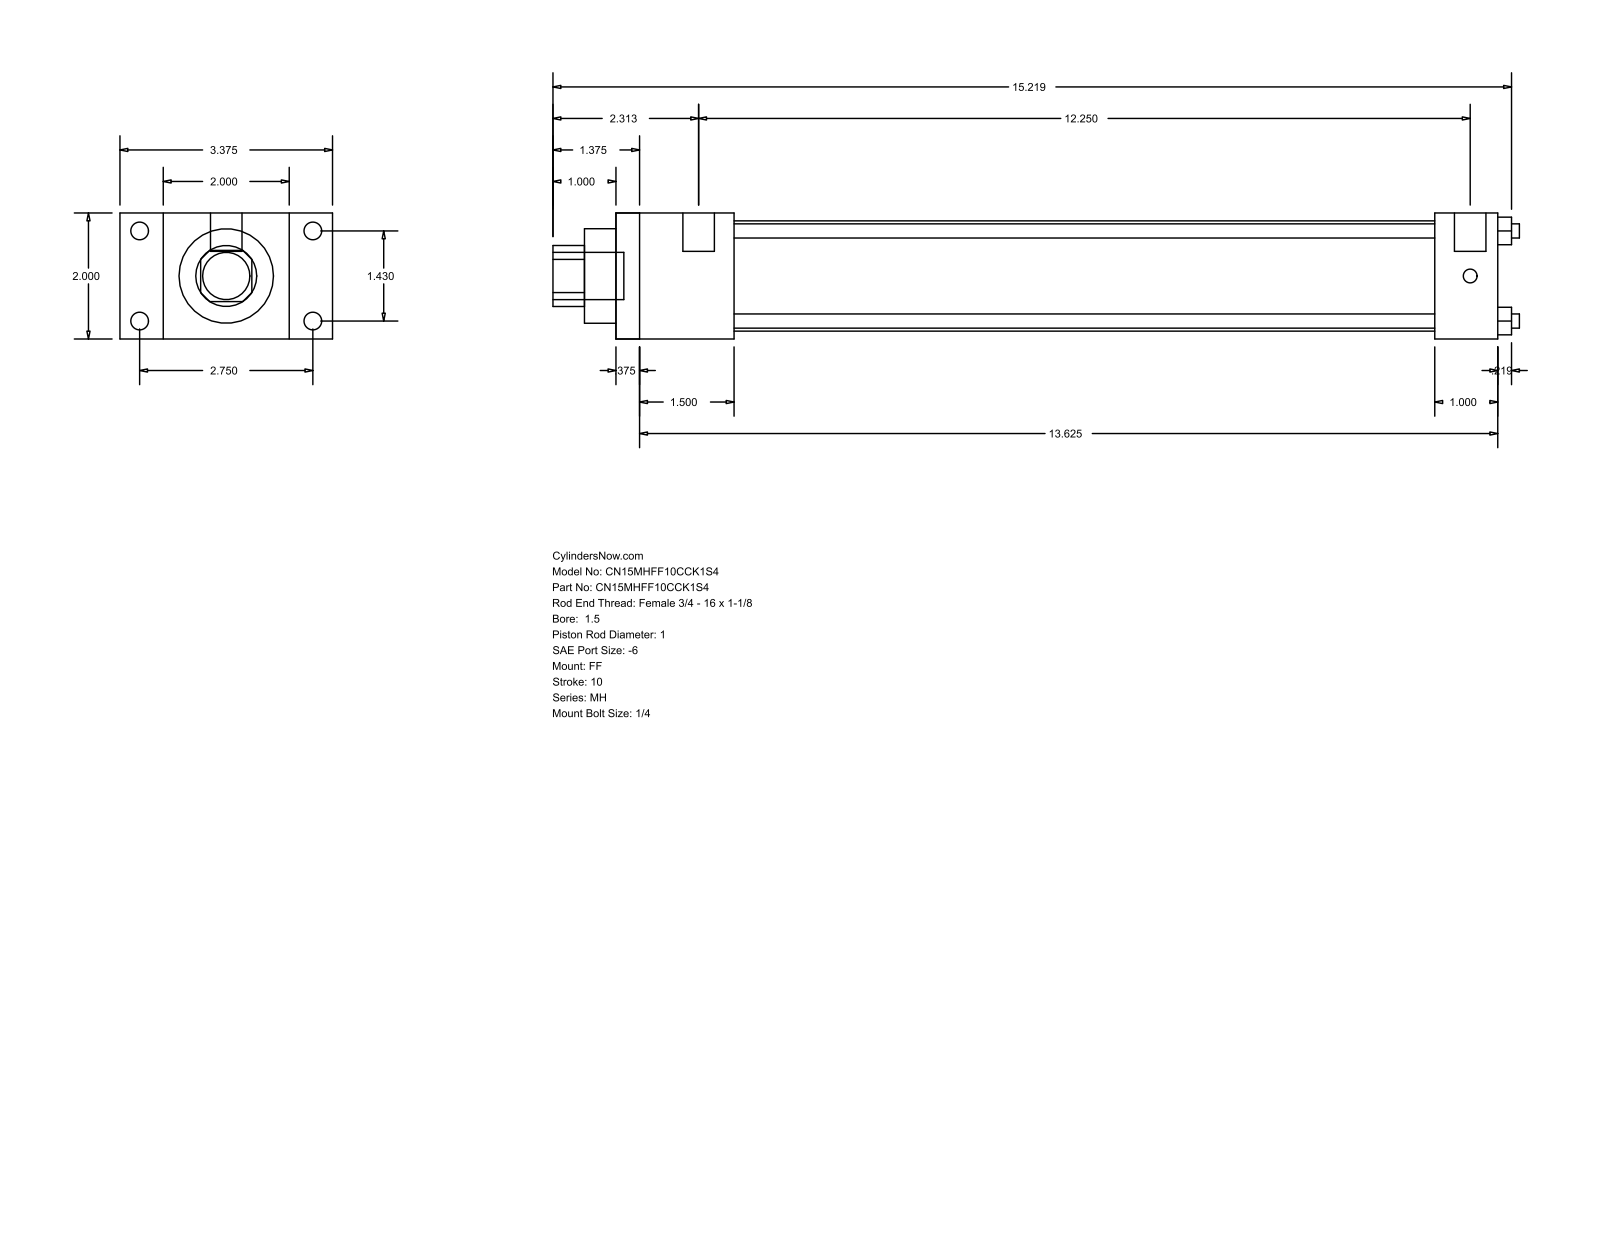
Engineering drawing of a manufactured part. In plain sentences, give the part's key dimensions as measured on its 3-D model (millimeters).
The part is named "MH_FF__0150_1". Its 3-D file was written by "GSSL Pune (CONFIG_CONTROL_DESIGN)". It is 0 solids with 92 faces: 64 planar, 28 cylindrical and 0 other. Overall it measures 389.73 by 85.72 by 50.8 millimeters. Round holes: 4 of diameter 5.71, 1 of diameter 25.4, 1 of diameter 38.1, 1 of diameter 44.45. Round bosses or shafts: 4 of diameter 7.14, 4 of diameter 5.56, 2 of diameter 12.7, 1 of diameter 19.05. Partial cylindrical surfaces (rounded edges, fillets, slot ends): 1 of radius 12.29. The main face-to-face distances are 50.8, 355.6, 9.52, 346.08, 25.4, 17.46, 68.26, 47.63, 38.11, 307.97. The hole center spacings are 25.68, 36.32, 51.36.
